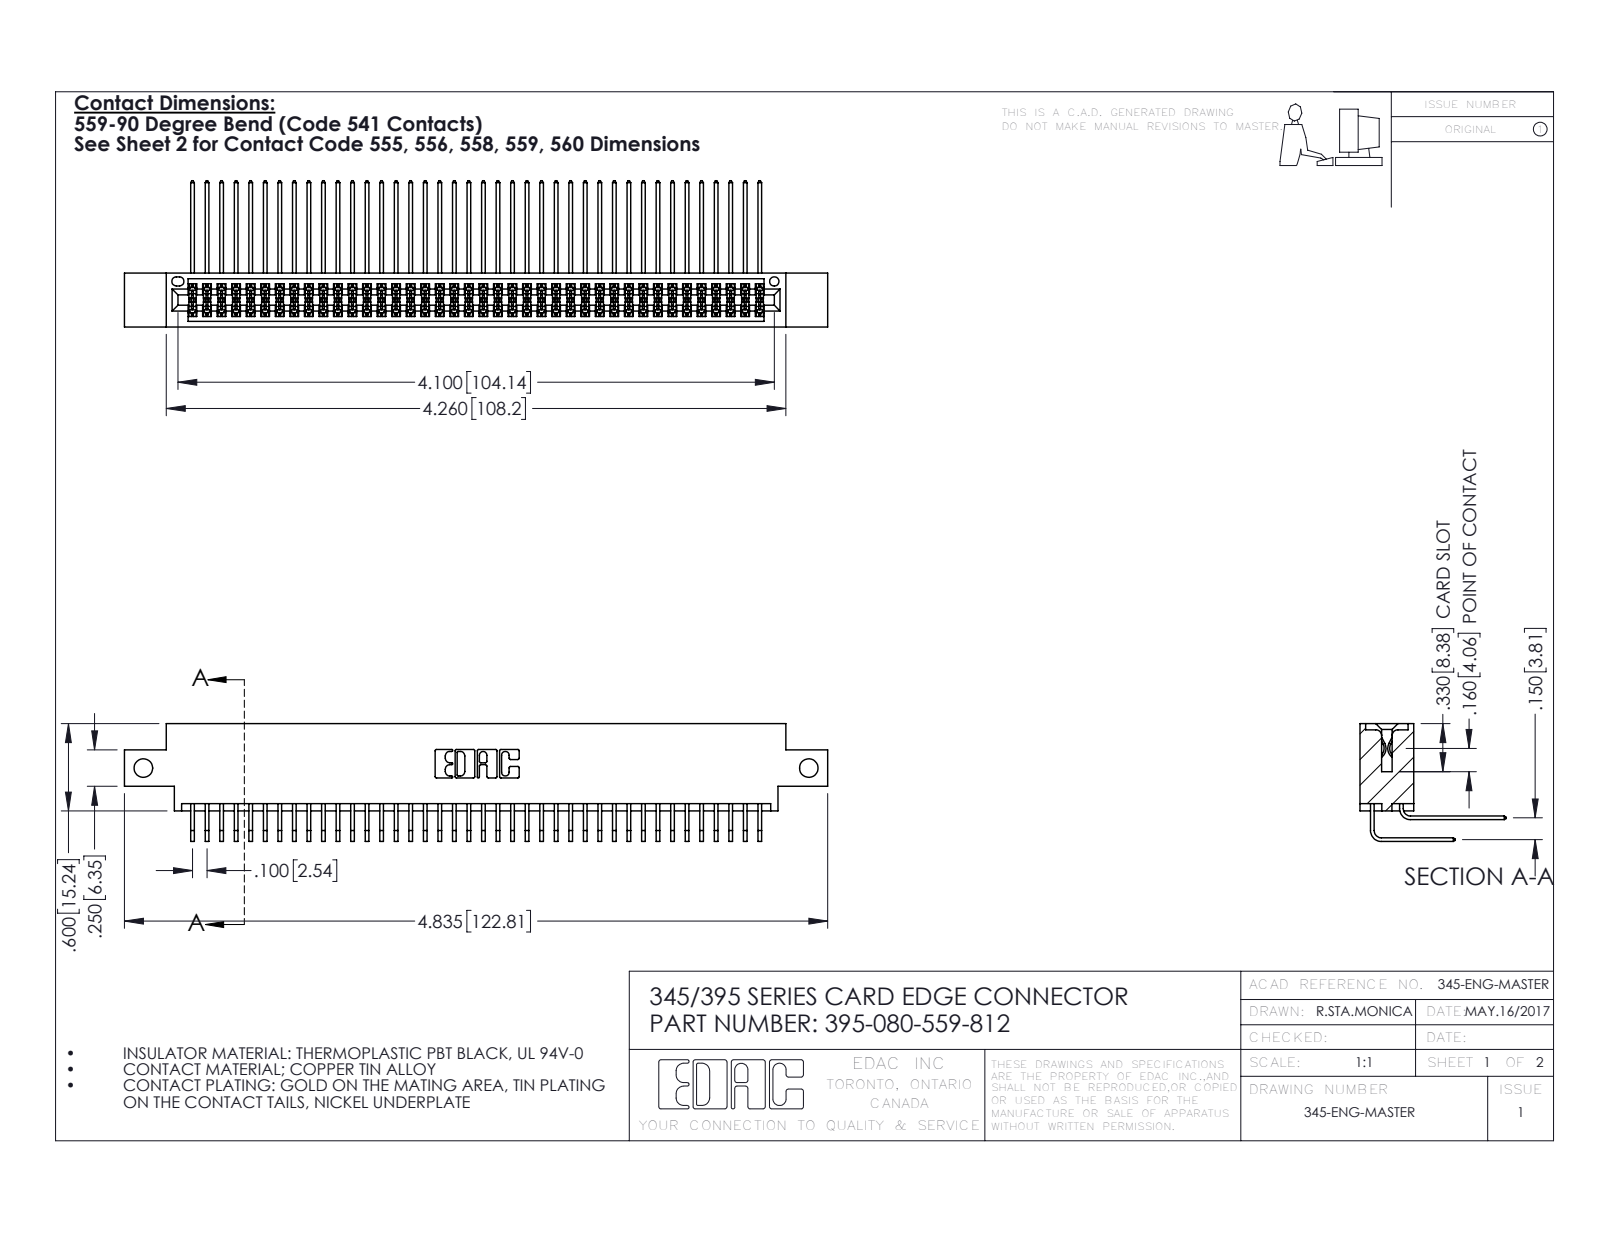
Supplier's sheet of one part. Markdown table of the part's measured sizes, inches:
| quantity | value |
| --- | --- |
| part name | 345-292-001_558 559 Tail - 1; 345-292-001_559 Tail - 2; 345 Part_0.170 Offset - Side Mount; 395-080-559-812 |
| STEP written by | SolidWorks 2016 (CONFIG_CONTROL_DESIGN) |
| units | inches |
| bodies | 81 solids, 4290 faces (2884 planar, 1406 cylindrical, 0 other) |
| overall size | 4.835 × 1.005 × 0.809 |
| volume | 0.743 in³ |
| surface area | 31.2 in² |
| round holes (diameter × count) | 0.128 × 2, 0.064 × 1 |
| partial cylindrical surfaces (radius × count) | 0.006 × 120, 0.01 × 22, 0.007 × 6, 0.031 × 6, 0.026 × 3, 0.014 × 2, 0.019 × 2, 0.022 × 2 |
| main face-to-face distances | 0.072, 0.298, 0.37, 0.2, 0.098, 0.272, 0.025, 0.225, 0.175, 0.15 |
| hole center spacings | 4.575 |
